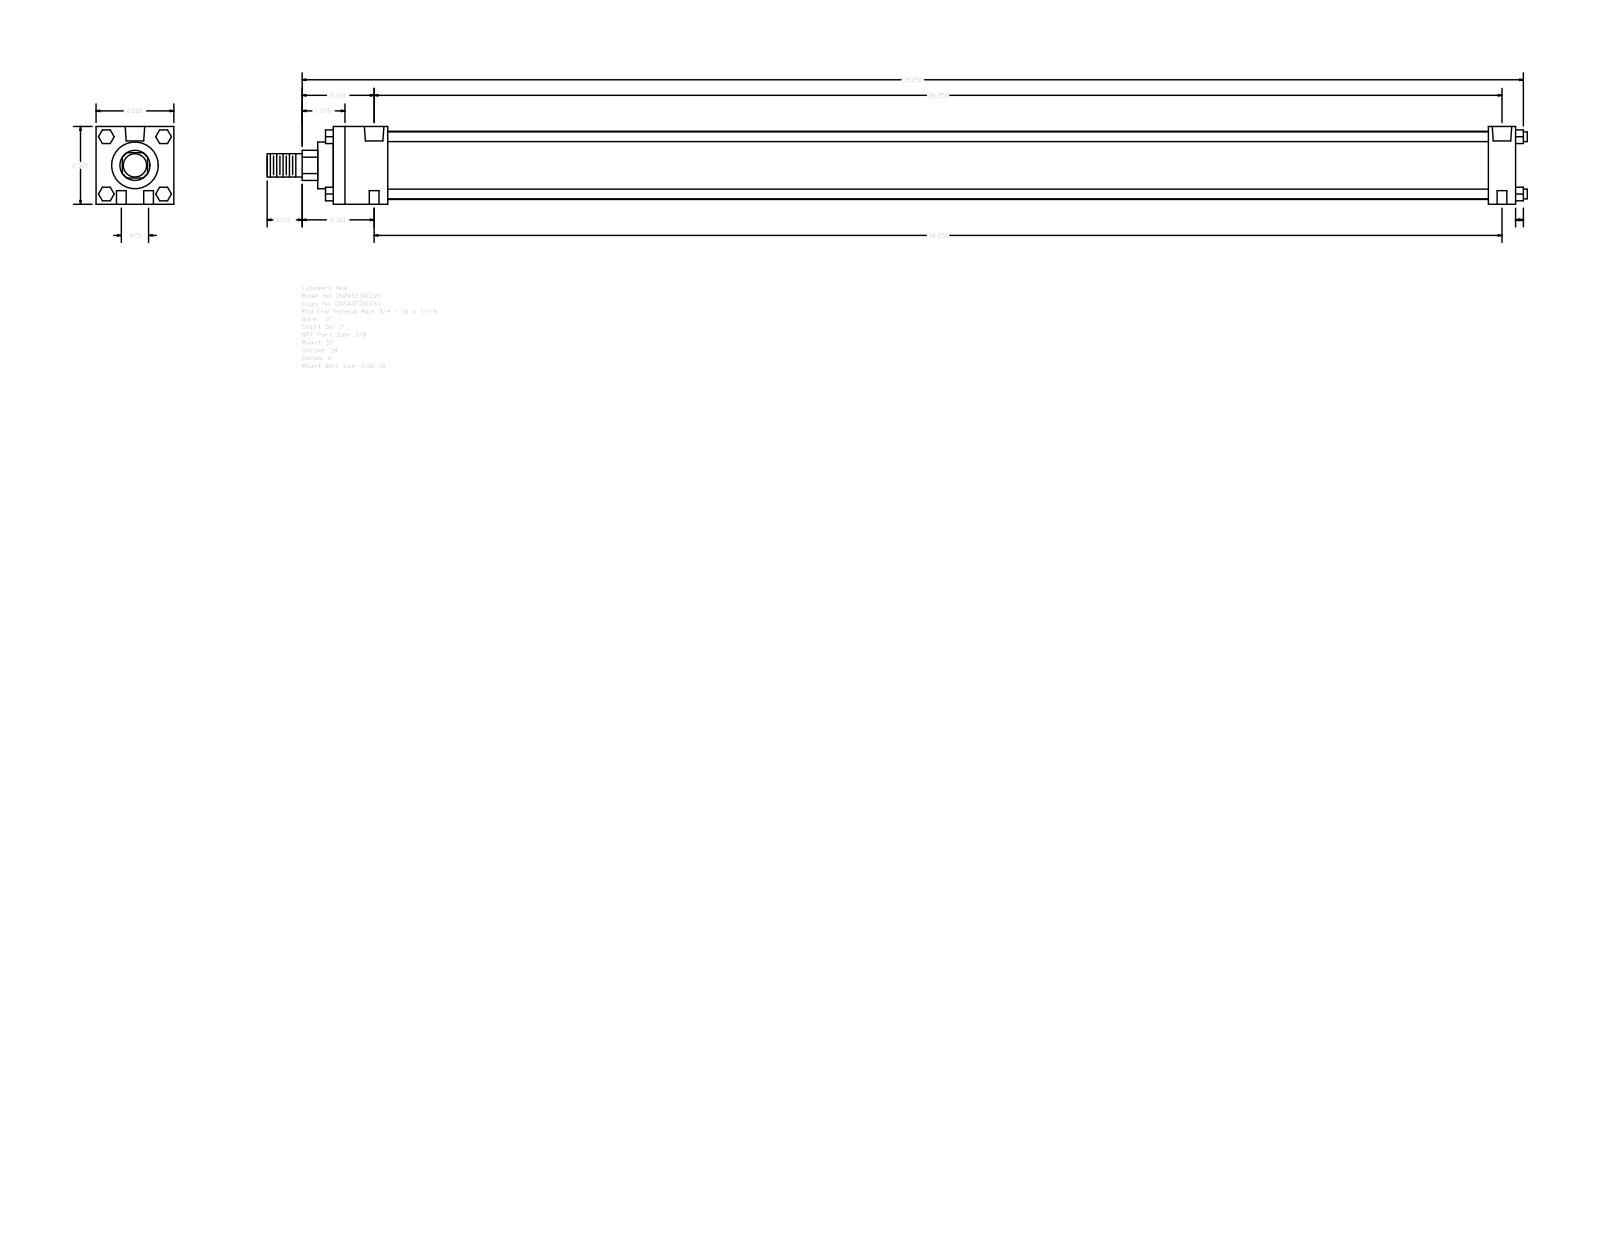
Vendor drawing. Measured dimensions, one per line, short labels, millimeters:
name: A_SF__0200_1
written by: GSSL Pune (CONFIG_CONTROL_DESIGN)
unit: mm
bodies: 0 solids, 124 faces (94 planar, 30 cylindrical, 0 other)
size: 1028.7 × 63.5 × 63.5
holes: 4× ⌀7.94, 2× ⌀5.56, 2× ⌀15.93
bosses: 4× ⌀7.94, 1× ⌀55.63, 1× ⌀38.1, 1× ⌀25.4, 1× ⌀19.05
rounds: 1× R12.29
face distances: 63.5, 965.2, 942.98, 22.22, 44.45, 898.53, 920.75, 12.7, 977.9, 6.35
hole spacings: 11.11, 920.82, 920.75, 22.22, 921.02, 915.18
